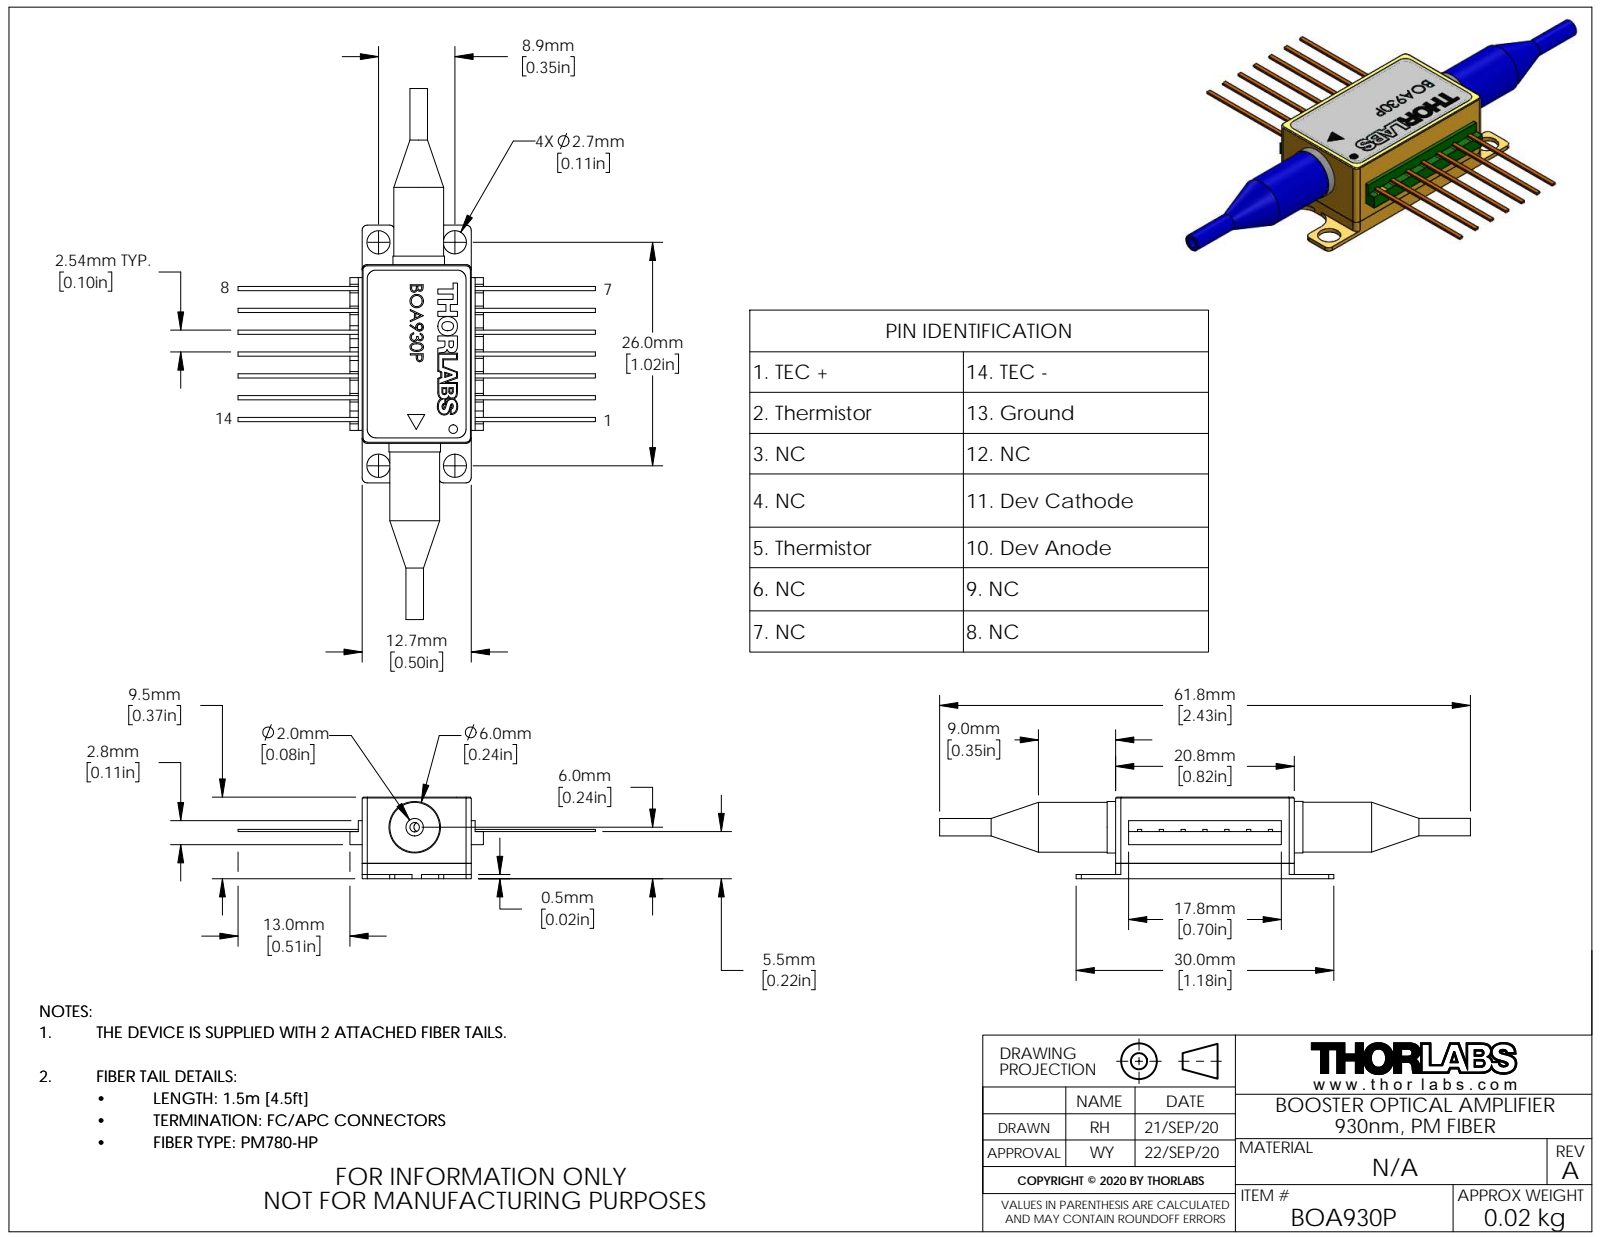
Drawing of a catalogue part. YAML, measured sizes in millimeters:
part_name: "QTN039466-E0W"
step_written_by: "SolidWorks 2018 (AUTOMOTIVE_DESIGN)"
units: millimeters
bodies: {solids: 0, faces: 385, planar: 264, cylindrical: 50, other: 71}
overall_size: [61.8, 41.6, 9.5]
round_holes:
  - {diameter: 2.7, count: 4}
  - {diameter: 1.1, count: 2}
  - {diameter: 1, count: 1}
round_bosses_or_shafts:
  - {diameter: 6, count: 2}
  - {diameter: 5.8, count: 2}
  - {diameter: 2.04, count: 2}
partial_cylinders:
  - {radius: 0.6, count: 12}
  - {radius: 0.5, count: 4}
  - {radius: 2, count: 4}
face_to_face_distances: [9.5, 12.7, 1.8, 7.7, 1.52, 5.49, 3.69, 4.01, 3.97, 2.17]
hole_center_spacings: [8.9, 26, 27.48, 0.46, 4.27, 9.69, 21.73, 23.41]
